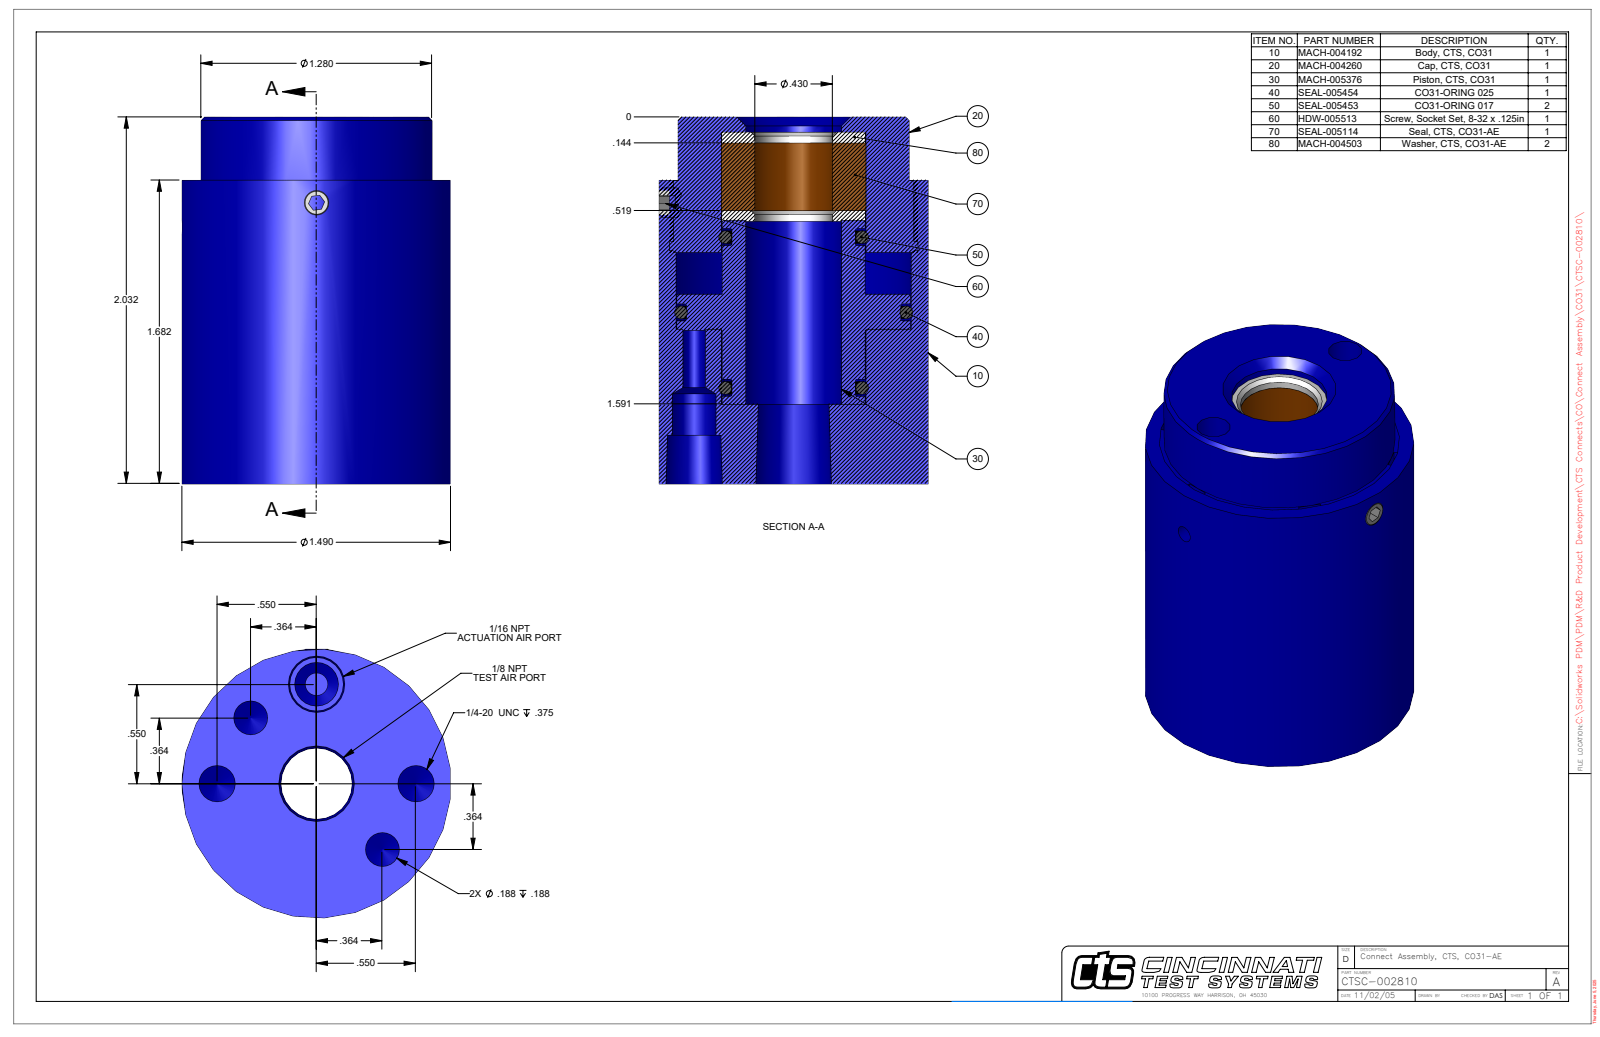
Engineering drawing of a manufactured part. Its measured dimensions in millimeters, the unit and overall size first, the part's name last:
Units: millimetres
Overall size (bounding box): 51.6 × 37.8 × 37.8
Round holes (diameter × count): ⌀4.7 ×4, ⌀5.1 ×2, ⌀2.4 ×1, ⌀3.5 ×1, ⌀6.1 ×1, ⌀10.9 ×1, ⌀11 ×1, ⌀13.5 ×1, ⌀20.3 ×1, ⌀33.8 ×1
Round bosses / shafts (diameter × count): ⌀37.8 ×1, ⌀32.5 ×1, ⌀20.1 ×1
Partial cylindrical surfaces — rounded edges, fillets, slot ends (radius × count): R17.4 ×1, R18.6 ×1
Main face-to-face distances: 51.6, 42.7, 8.9, 3.2, 8, 34.7, 43.6, 11.2, 31.5, 40.4
Hole centre spacings: 13.1, 10.4, 14, 25, 0.9, 10, 19.2, 19.8
Volume: 48 280 mm³ · Surface area: 11 070 mm²
Bodies: 1 solid, 111 faces (53 planar, 40 cylindrical, 18 other)
Part name (STEP PRODUCT): CTSC-002810
STEP written by: SolidWorks 2023 (AUTOMOTIVE_DESIGN)
